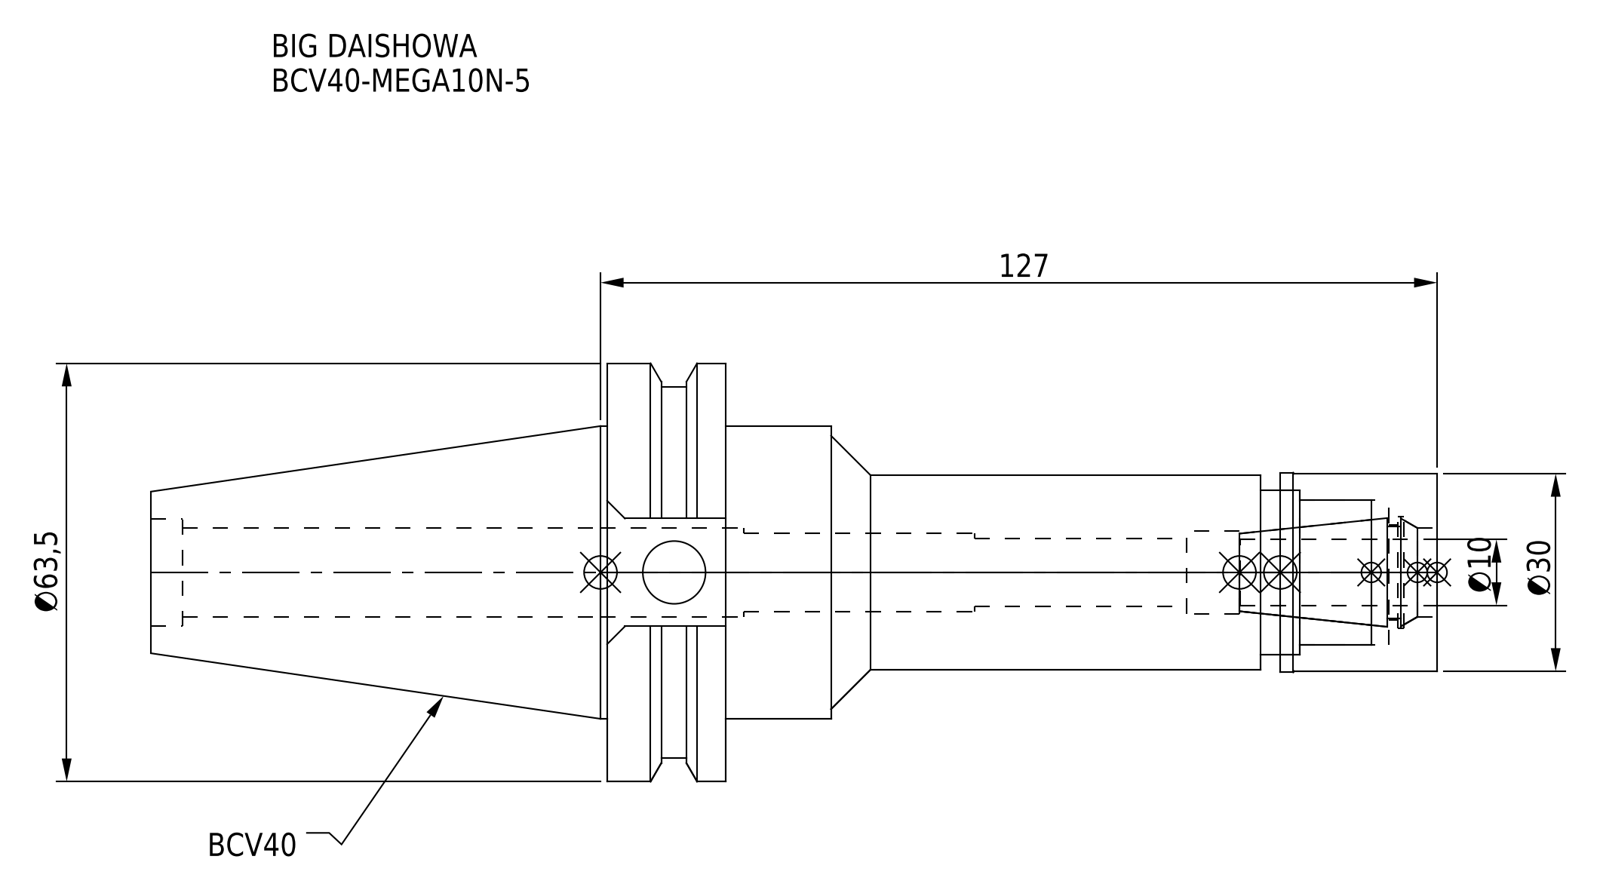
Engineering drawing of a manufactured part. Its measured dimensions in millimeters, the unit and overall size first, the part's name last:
Units: millimetres
Overall size (bounding box): 195.25 × 63.5 × 61.35
Round holes (diameter × count): ⌀9.53 ×1, ⌀10.4 ×1, ⌀12 ×1, ⌀12.5 ×1, ⌀13.5 ×1, ⌀13.6 ×1, ⌀14.5 ×1, ⌀16.32 ×1, ⌀17 ×1, ⌀22 ×1, ⌀25 ×1
Round bosses / shafts (diameter × count): ⌀63.5 ×1, ⌀56.36 ×1, ⌀44.45 ×1, ⌀30.3 ×1, ⌀30 ×1, ⌀29.5 ×1
Main face-to-face distances: 18.05, 107.95, 126, 195.25, 87.3, 69.25, 47.55, 23.8, 84.15, 102.2
Volume: 179 984 mm³ · Surface area: 38 376 mm²
Bodies: 2 solids, 91 faces (33 planar, 44 cylindrical, 14 other)
Part name (STEP PRODUCT): DXF_TEMP_ASSY_ASM_4_ASM.stp; BCV40-MEGA10N-5_1.stp; BCV40-MEGA10N-5-100.stp; BCV40MN10050-100_ASM.stp (+3 more)
STEP written by: SolidWorks 2019 (CONFIG_CONTROL_DESIGN)
